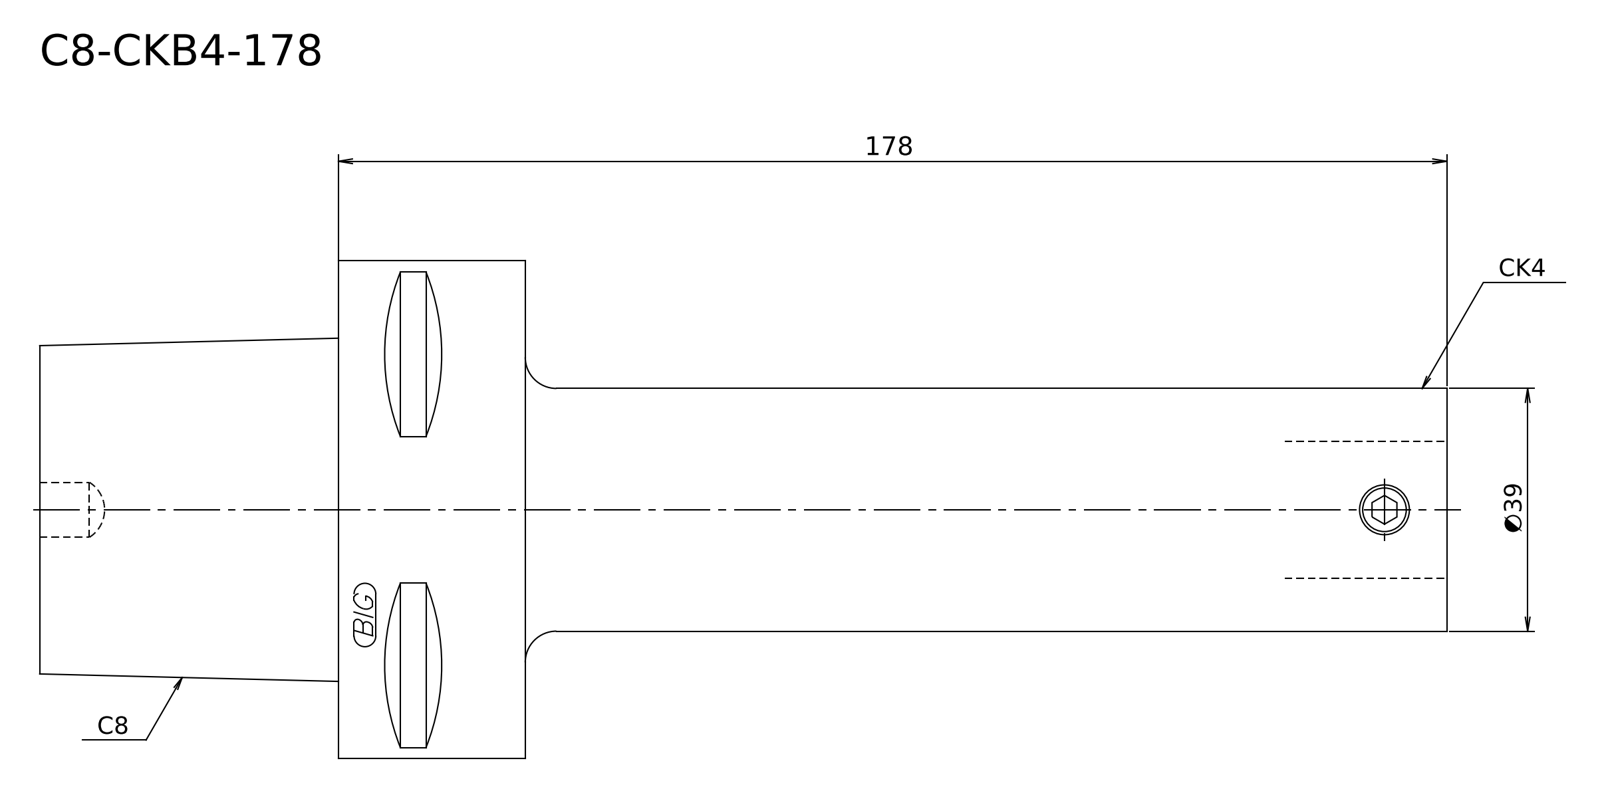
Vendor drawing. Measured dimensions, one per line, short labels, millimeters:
written by: Kubotek KeyCreator V8.5.1 (14335) (CONFIG_CONTROL_DESIGN)
unit: mm
bodies: 1 solid, 8 faces (4 planar, 2 cylindrical, 2 other)
size: 226 × 79.98 × 79.98
volume: 435 615 mm³; area: 43 328 mm²
bosses: 1× ⌀79.98, 1× ⌀39
face distances: 30, 78, 48, 148, 178, 226
